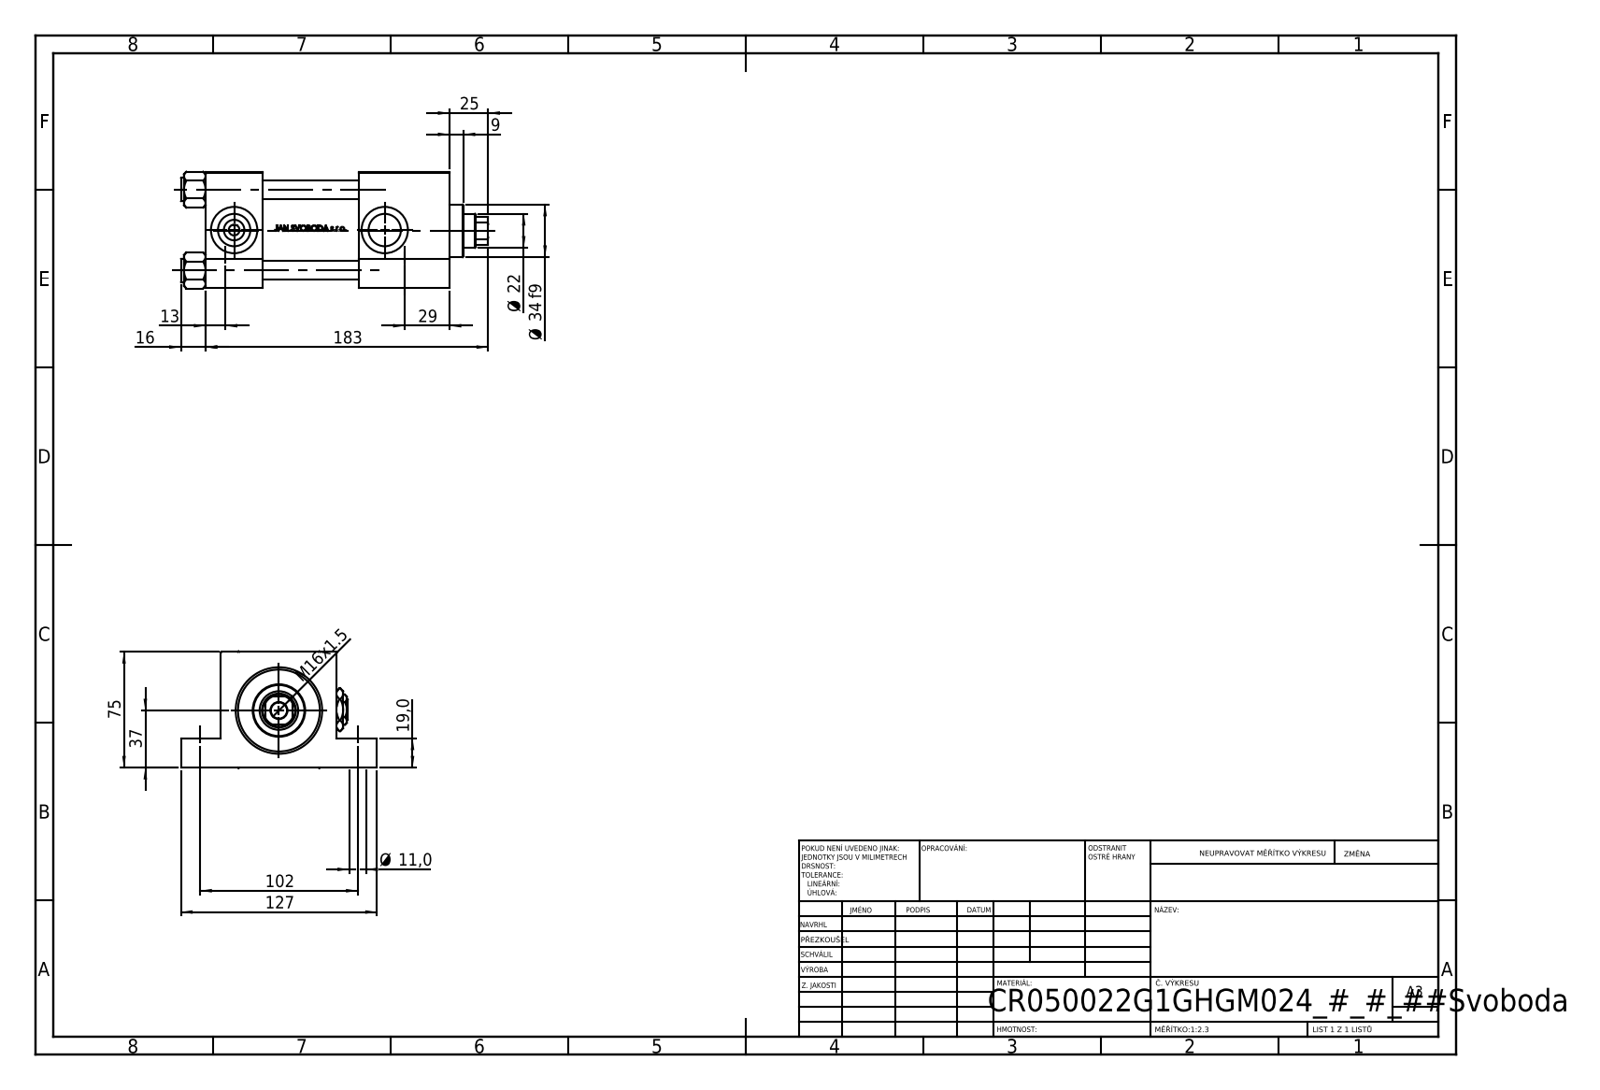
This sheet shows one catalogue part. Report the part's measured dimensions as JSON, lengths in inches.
{"part_name": "NUT_M5_G; V215CR_G_TYCINKA; V215_VC_A; Zatka_pro_OIL_PORT (+2 more)", "step_written_by": "SolidWorks 2019 (CONFIG_CONTROL_DESIGN)", "units": "inches", "bodies": {"solids": 12, "faces": 1134, "planar": 454, "cylindrical": 128, "other": 552}, "overall_size": [7.835, 5, 2.974], "volume_in3": 46.24, "surface_area_in2": 253.4, "round_holes": [[0.433, 4], [0.472, 4], [0.276, 2], [0.825, 2], [1.181, 2], [0.413, 1], [0.866, 1], [0.984, 1], [1.614, 1], [1.969, 1], [2.087, 1]], "round_bosses_or_shafts": [[0.591, 4], [2.205, 1], [1.339, 1]], "partial_cylinders_radius": [[0.413, 1]], "face_to_face_distances": [2.953, 1.457, 6.22, 4.764, 0.748, 2.205, 3.898, 2.441, 2.323, 1.024], "hole_center_spacings": [2.059, 1.442, 1.47, 2.912, 4.016, 4.567, 6.081, 3.839]}
